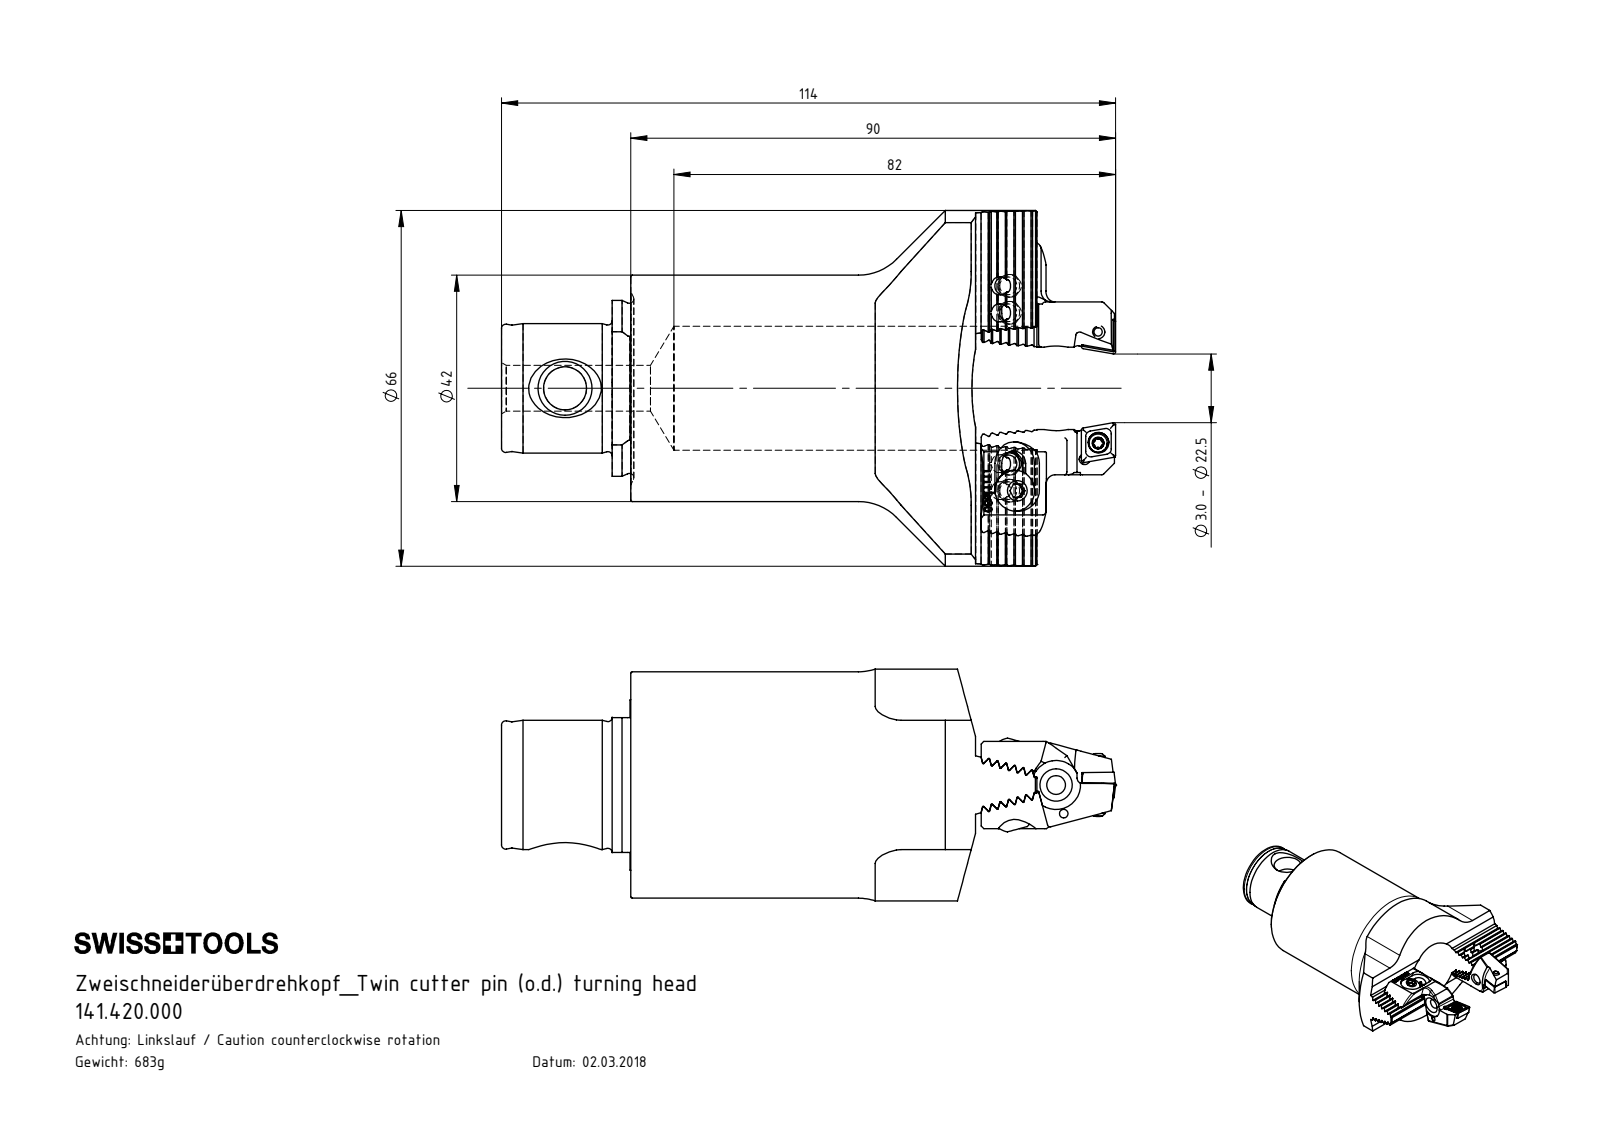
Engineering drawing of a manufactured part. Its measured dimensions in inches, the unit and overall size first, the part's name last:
Units: inches
Overall size (bounding box): 4.488 × 2.598 × 1.693
Round holes (diameter × count): ⌀0.13 ×4, ⌀0.165 ×4, ⌀0.063 ×2, ⌀0.079 ×2, ⌀0.081 ×2, ⌀0.11 ×2, ⌀0.152 ×2, ⌀0.169 ×2, ⌀0.138 ×1, ⌀0.315 ×1, ⌀0.335 ×1, ⌀0.358 ×1
Round bosses / shafts (diameter × count): ⌀0.299 ×2, ⌀0.283 ×2, ⌀0.157 ×2, ⌀0.134 ×2, ⌀0.098 ×2, ⌀1.654 ×1, ⌀0.945 ×1
Partial cylindrical surfaces — rounded edges, fillets, slot ends (radius × count): R0.005 ×26, R0.02 ×16, R0.008 ×12, R0.014 ×10, R0.039 ×4, R0.079 ×4, R0.091 ×4, R0.157 ×4
Main face-to-face distances: 0.056, 0.113, 0.169, 0.225, 0.945, 0.281, 2.52, 3.465, 0.055, 0.058
Hole centre spacings: 0.197, 0.154, 0.157, 0.217, 0.796, 0.919, 0.922, 0.418
Volume: 5.325 in³ · Surface area: 38.36 in²
Bodies: 11 solids, 945 faces (442 planar, 236 cylindrical, 267 other)
Part name (STEP PRODUCT): 141.420.000; Z20-ER1.001.008; Z20-ER1.003.008_A_gespannt; Z20-ER1.002.008_A (+5 more)
STEP written by: SolidWorks 2017 (CONFIG_CONTROL_DESIGN)
